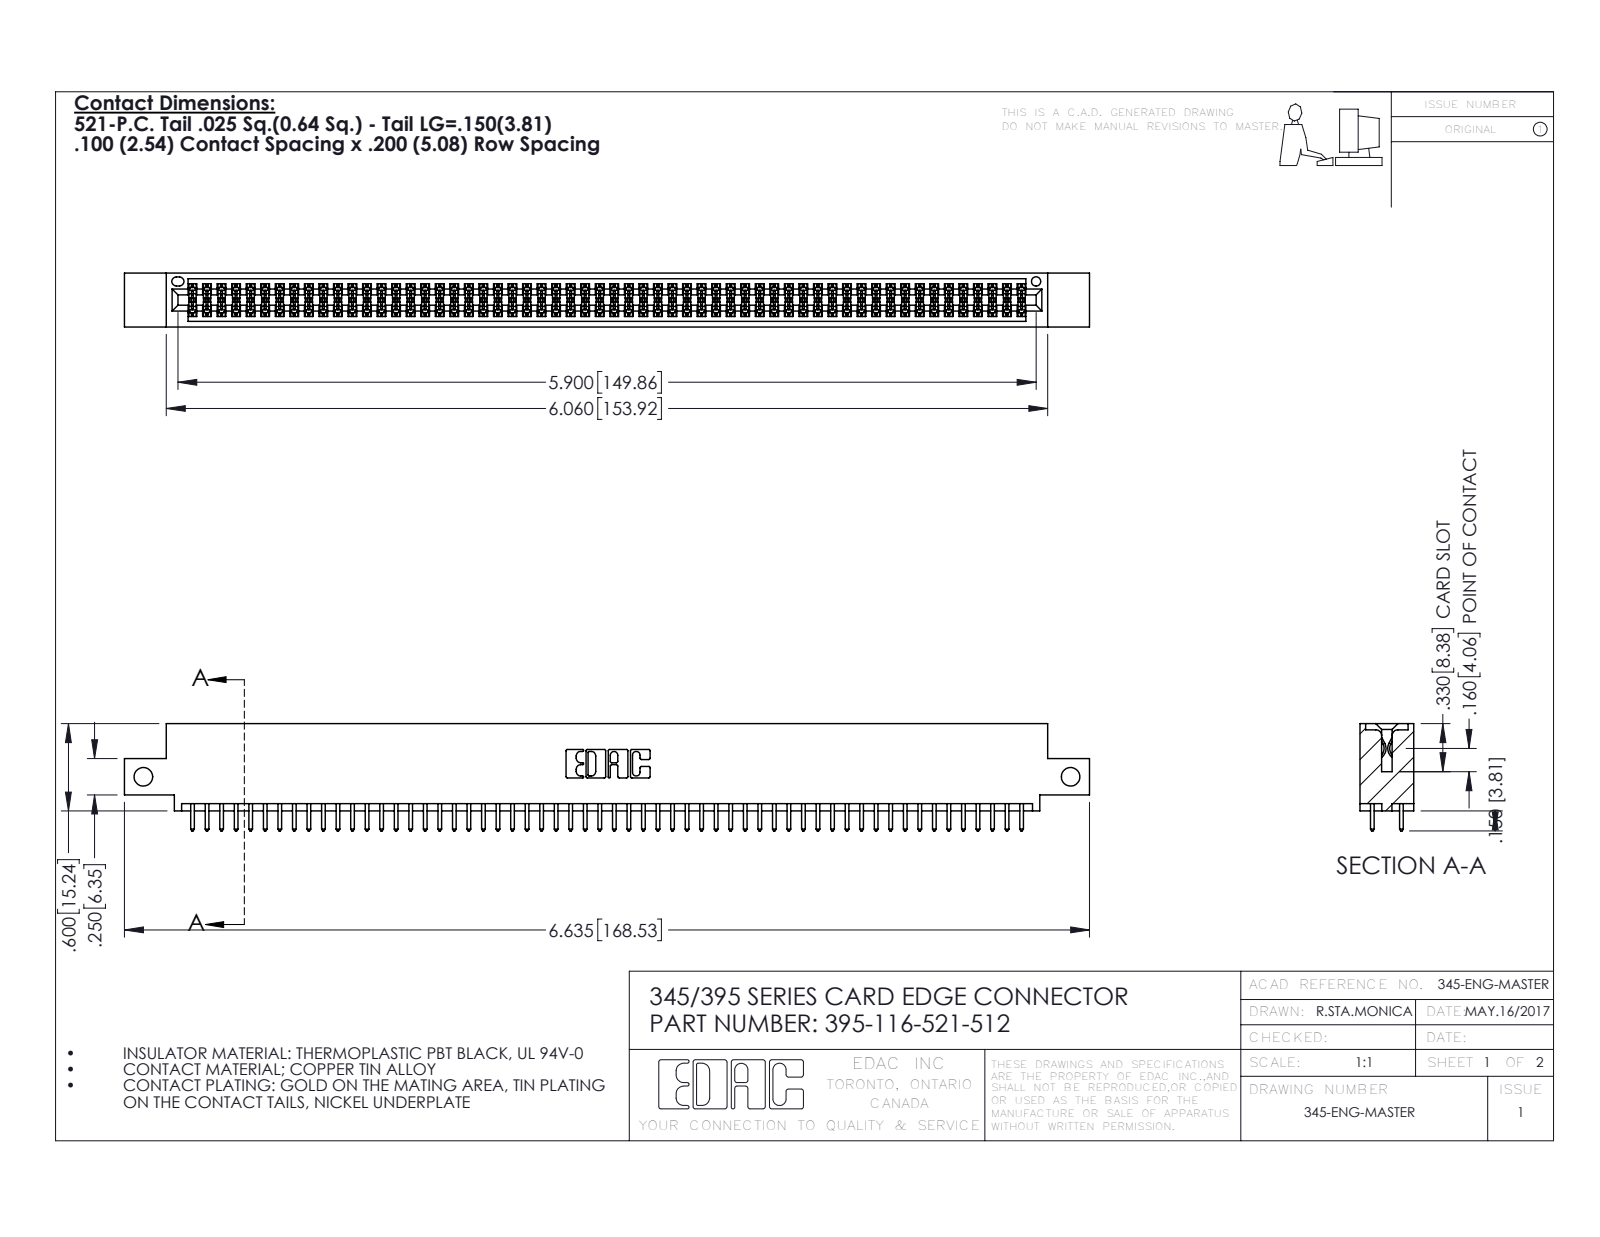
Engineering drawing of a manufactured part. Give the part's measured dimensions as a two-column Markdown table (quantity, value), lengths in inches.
| quantity | value |
| --- | --- |
| part name | 345 Part_0.110 Offset - Side Mount; 345-292-001_345-293-121; 395-116-521-512 |
| STEP written by | SolidWorks 2016 (CONFIG_CONTROL_DESIGN) |
| units | inches |
| bodies | 117 solids, 5930 faces (3912 planar, 2018 cylindrical, 0 other) |
| overall size | 6.635 × 0.737 × 0.37 |
| volume | 0.995 in³ |
| surface area | 37.31 in² |
| round holes (diameter × count) | 0.128 × 2, 0.064 × 1 |
| partial cylindrical surfaces (radius × count) | 0.006 × 174, 0.01 × 116, 0.01 × 22, 0.007 × 6, 0.031 × 6, 0.026 × 3, 0.014 × 2, 0.019 × 2 |
| main face-to-face distances | 0.298, 0.072, 0.2, 0.098, 0.272, 0.025, 0.37, 0.225, 0.175, 0.149 |
| hole center spacings | 6.375 |
